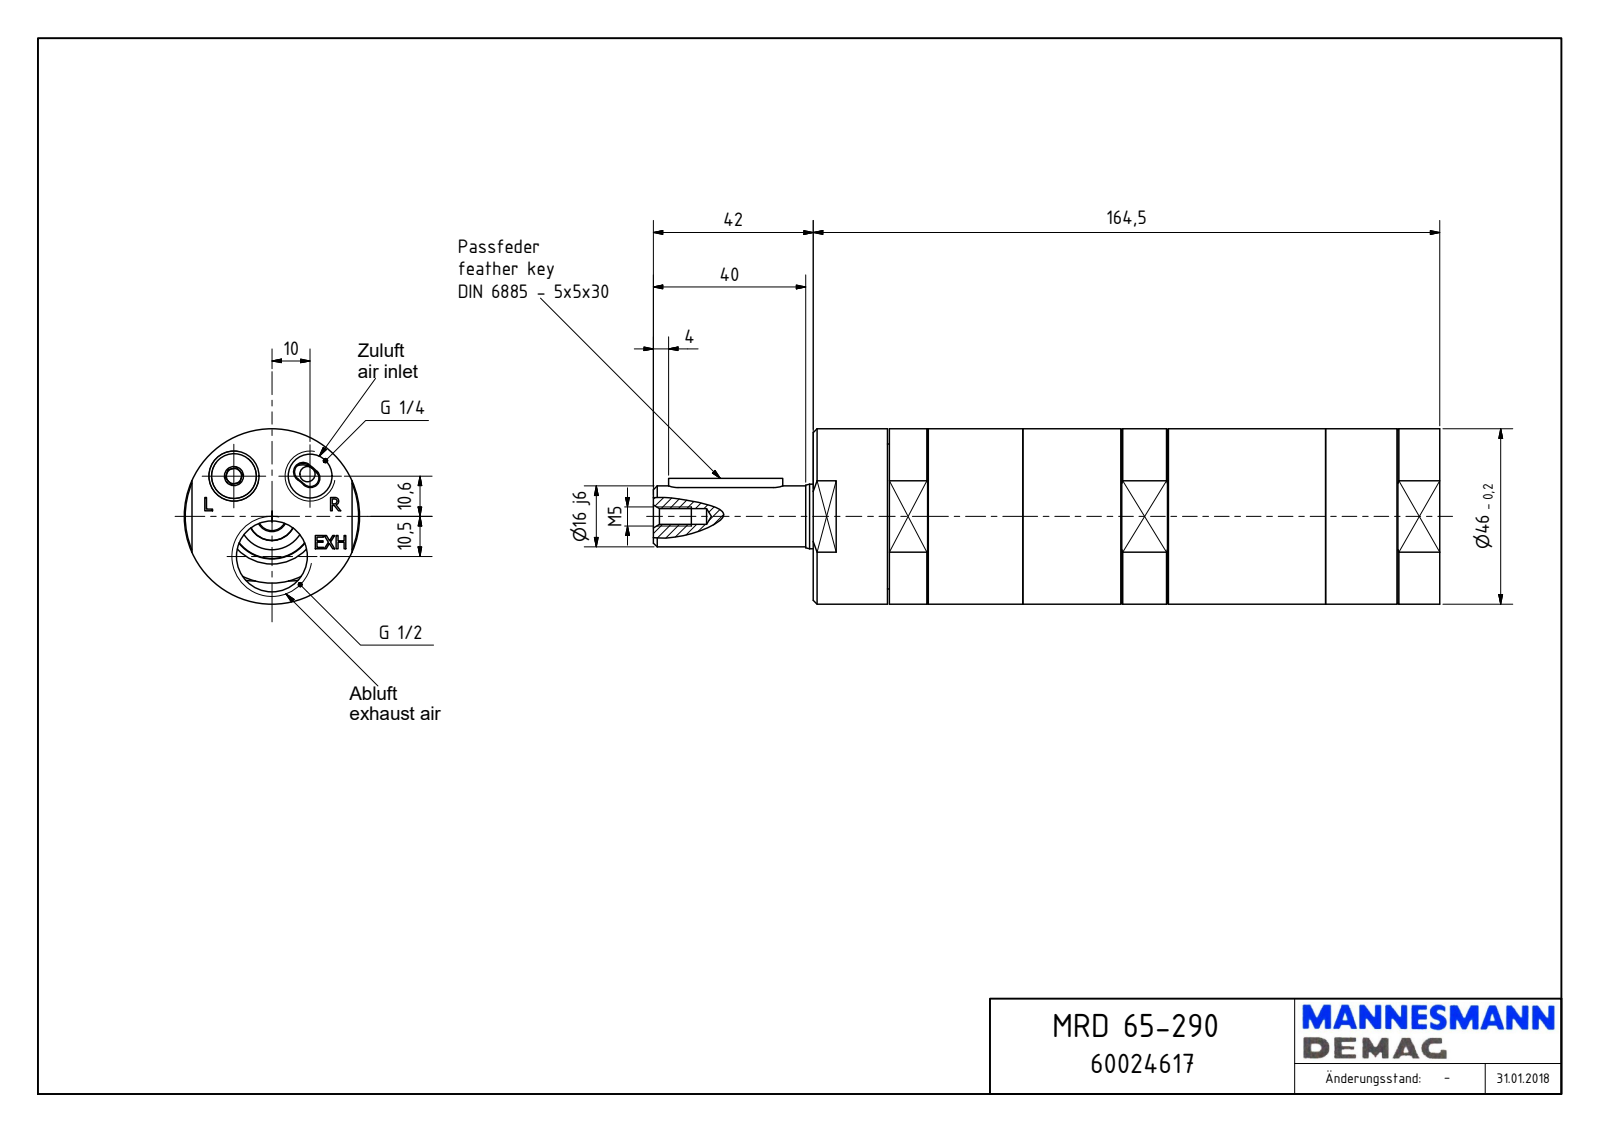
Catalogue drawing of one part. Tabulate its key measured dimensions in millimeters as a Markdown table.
| quantity | value |
| --- | --- |
| part name | MRD 65-290_60024617 |
| STEP written by | Autodesk Inventor 2018 (AUTOMOTIVE_DESIGN) |
| units | millimeters |
| bodies | 1 solid, 184 faces (113 planar, 35 cylindrical, 36 other) |
| overall size | 206.5 × 46 × 46 |
| volume | 275 896 mm³ |
| surface area | 33 704 mm² |
| round holes (diameter × count) | 4 × 1, 4.13 × 1, 11.45 × 1, 17.5 × 1, 18.63 × 1, 38 × 1, 38.38 × 1, 42 × 1 |
| round bosses / shafts (diameter × count) | 46 × 1, 41.76 × 1, 33.25 × 1, 16.95 × 1, 16 × 1 |
| partial cylindrical surfaces (radius × count) | 2.5 × 2, 5 × 2, 5.72 × 1 |
| main face-to-face distances | 164.5, 42, 144.5, 20, 19.5, 0.5, 145, 157.47, 137.97, 137.47 |
| hole center spacings | 14.57, 23.35, 10.5, 20 |
